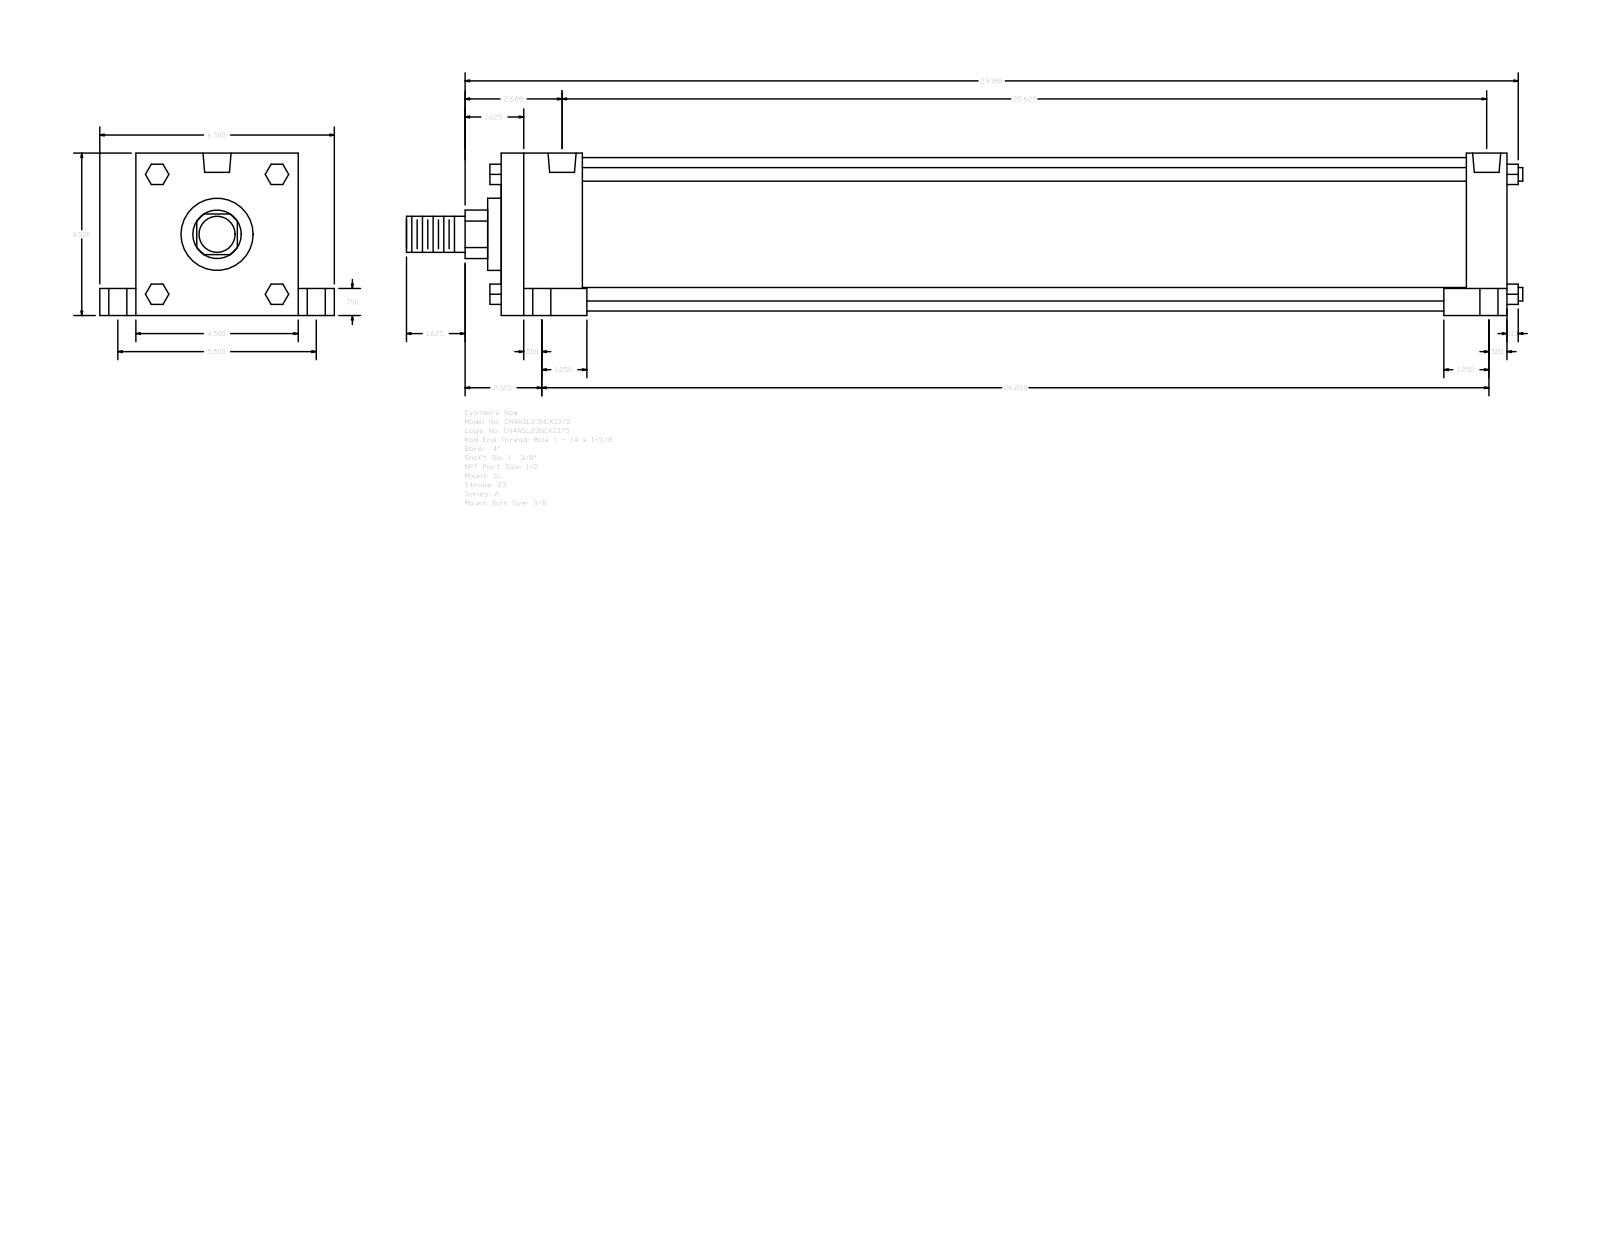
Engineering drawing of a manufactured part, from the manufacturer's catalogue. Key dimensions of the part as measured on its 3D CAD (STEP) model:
Part name (STEP PRODUCT): A_SL__0400_1.375
STEP written by: GSSL Pune (CONFIG_CONTROL_DESIGN)
Units: millimetres
Bodies: 0 solids, 150 faces (114 planar, 36 cylindrical, 0 other)
Overall size (bounding box): 785.81 × 165.1 × 114.3
Round holes (diameter × count): ⌀8.73 ×4, ⌀12.7 ×4, ⌀19.05 ×4, ⌀19.77 ×2
Round bosses / shafts (diameter × count): ⌀9.53 ×4, ⌀107.95 ×1, ⌀50.8 ×1, ⌀34.92 ×1, ⌀25.4 ×1
Partial cylindrical surfaces — rounded edges, fillets, slot ends (radius × count): R17.06 ×1
Main face-to-face distances: 114.3, 708.02, 57.15, 28.57, 25.4, 650.87, 679.45, 622.3, 139.7, 19.05
Hole centre spacings: 3.18, 69.87, 70.01, 71.29, 72, 139.7, 644.52, 647.7
